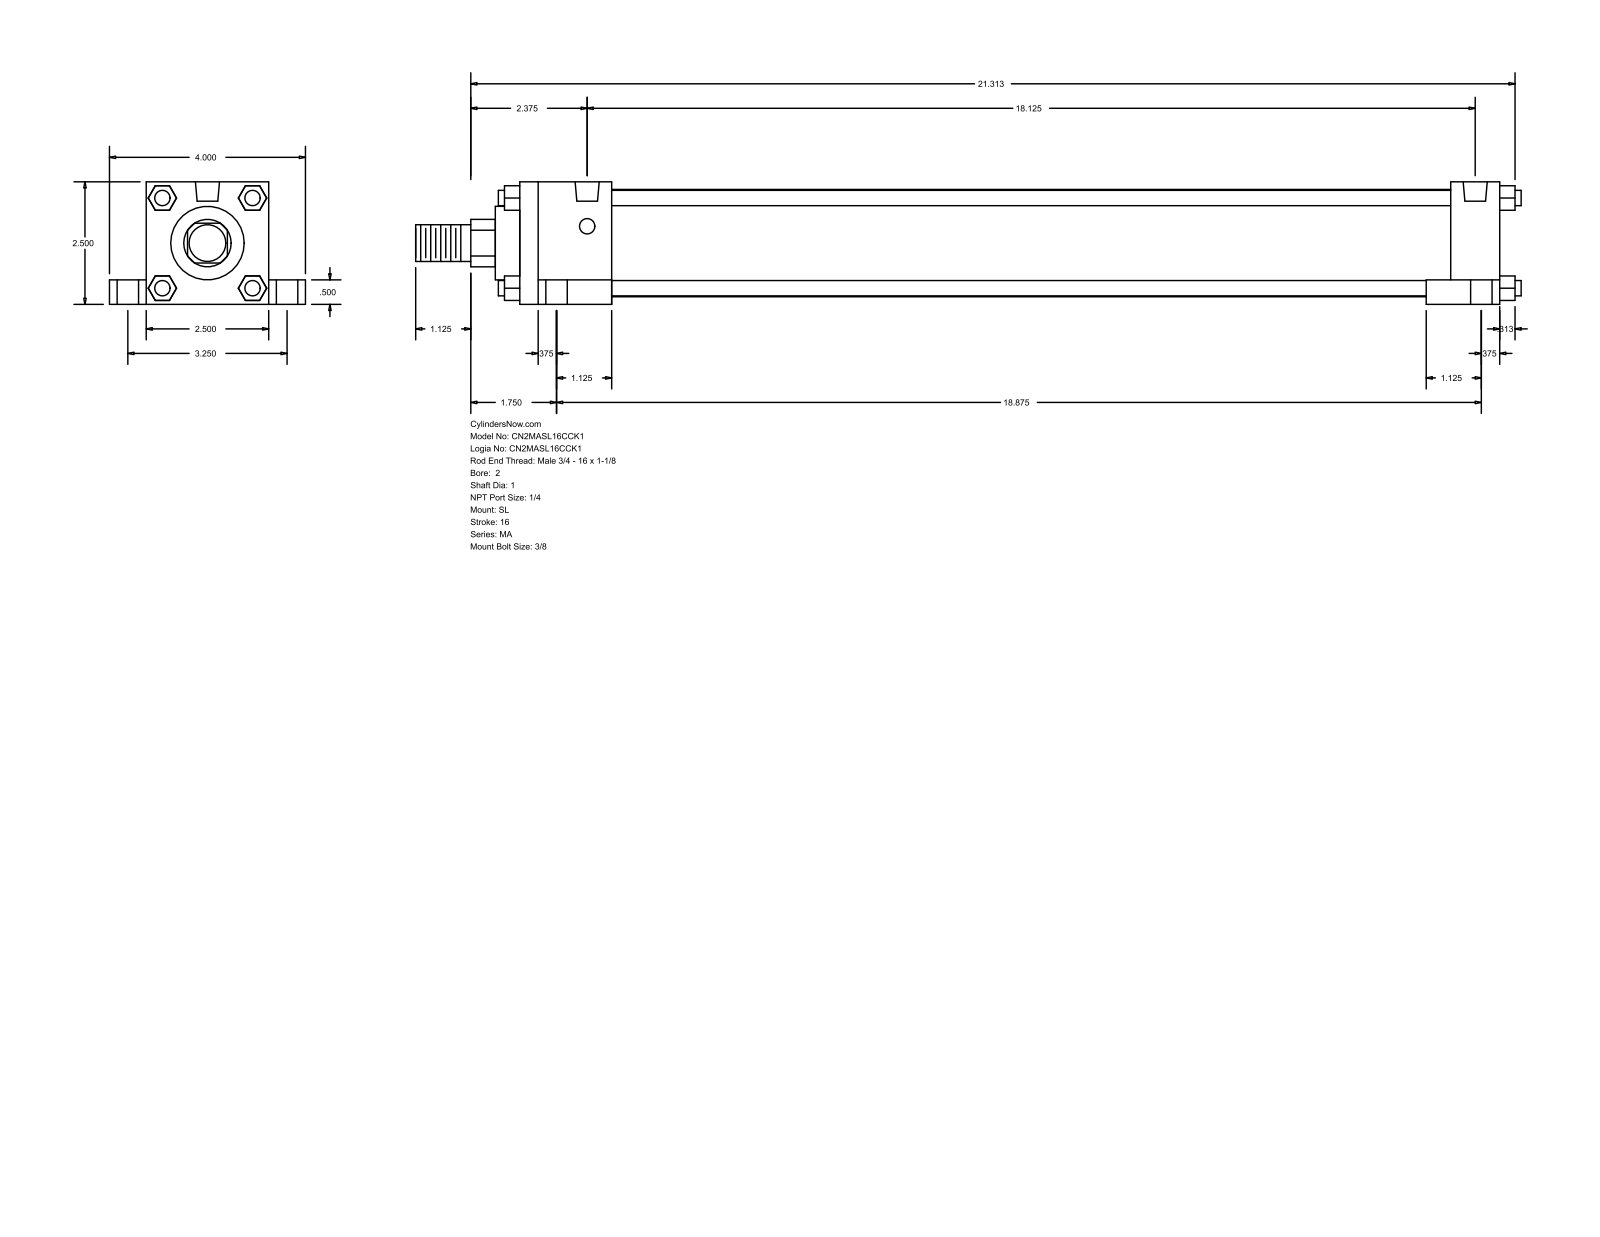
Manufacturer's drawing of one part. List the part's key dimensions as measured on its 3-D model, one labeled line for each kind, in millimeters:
Part name (STEP PRODUCT): MA_SL__0200_1
STEP written by: GSSL Pune (CONFIG_CONTROL_DESIGN)
Units: millimetres
Bodies: 0 solids, 148 faces (112 planar, 36 cylindrical, 0 other)
Overall size (bounding box): 573.09 × 101.6 × 63.5
Round holes (diameter × count): ⌀7.94 ×4, ⌀11.11 ×4, ⌀17.46 ×4, ⌀12.49 ×2
Round bosses / shafts (diameter × count): ⌀7.94 ×4, ⌀55.63 ×1, ⌀38.1 ×1, ⌀25.4 ×1, ⌀19.05 ×1
Partial cylindrical surfaces — rounded edges, fillets, slot ends (radius × count): R12.29 ×1
Main face-to-face distances: 63.5, 12.7, 508, 19.05, 82.55, 25.4, 50.8, 47.63, 460.37, 482.6
Hole centre spacings: 41.39, 44.22, 82.54, 460.37, 465.38, 478.03, 479.43, 486.48
